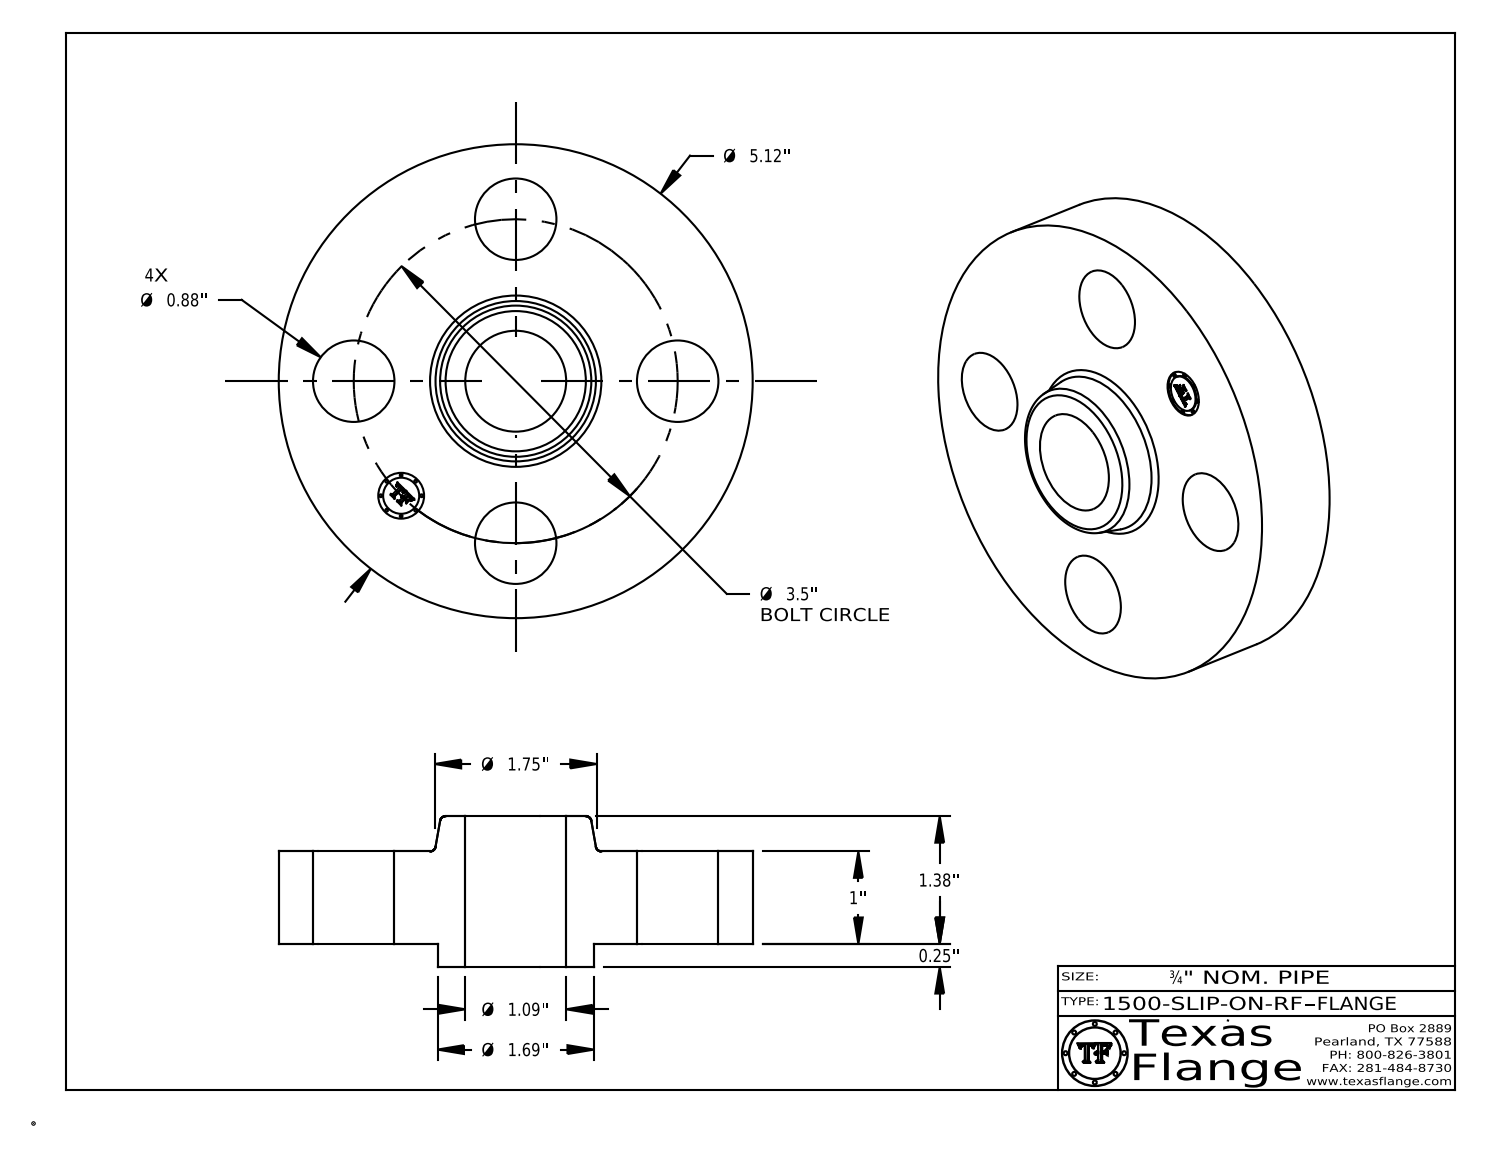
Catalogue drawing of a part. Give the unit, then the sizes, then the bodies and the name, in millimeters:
Units: millimetres
Overall size (bounding box): 130 × 130 × 41.4
Round holes (diameter × count): ⌀22.4 ×4, ⌀12.6 ×1, ⌀27.7 ×1
Round bosses / shafts (diameter × count): ⌀0.8 ×8, ⌀130 ×1, ⌀42.9 ×1, ⌀9.9 ×1
Main face-to-face distances: 25.4, 6.4, 31.8, 41.4, 35.1, 9.7, 0.4, 31.4, 25, 10
Hole centre spacings: 44.5, 62.9, 34, 82.1, 88.9
Volume: 295 600 mm³ · Surface area: 45 230 mm²
Bodies: 1 solid, 409 faces (369 planar, 34 cylindrical, 6 other)
Part name (STEP PRODUCT): 1500-SLIP-ON-RF
STEP written by: CATIA V5 STEP AP214 (AUTOMOTIVE_DESIGN)
